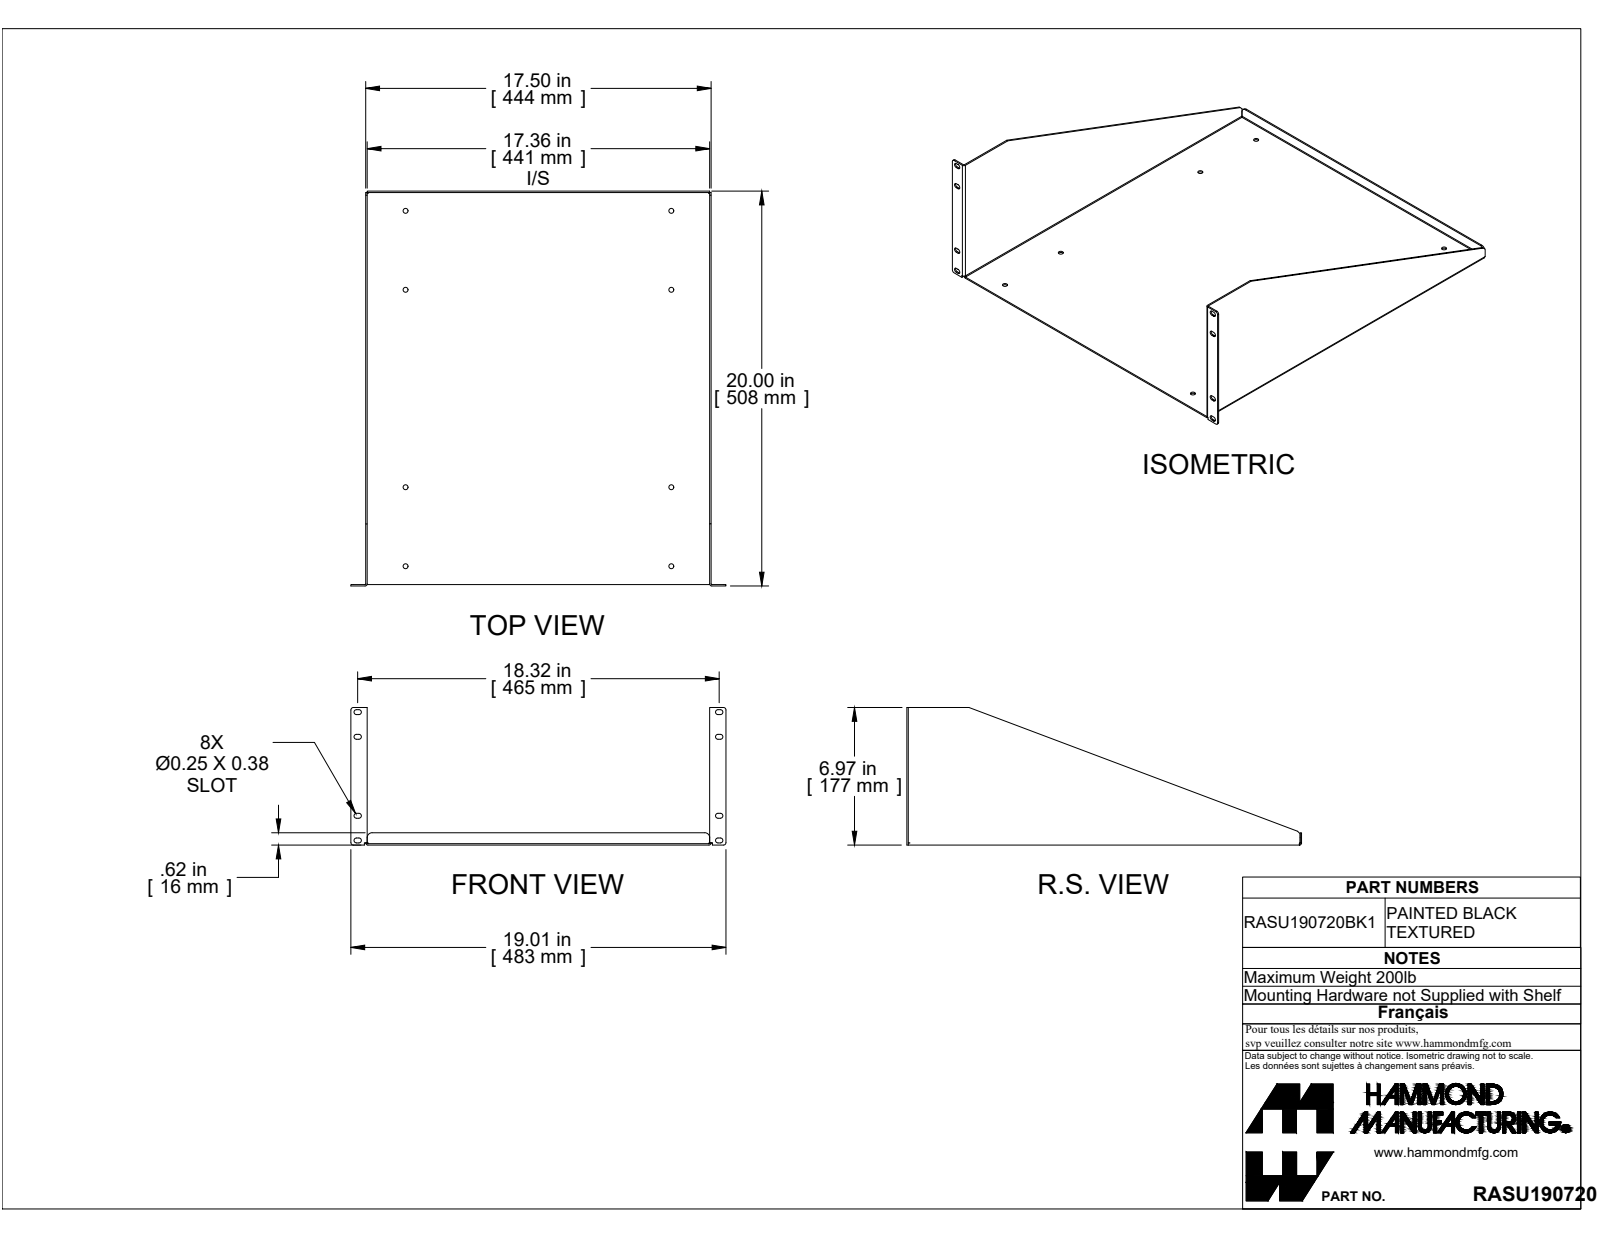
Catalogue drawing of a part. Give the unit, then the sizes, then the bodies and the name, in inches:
Units: inches
Overall size (bounding box): 20 × 19.006 × 6.968
Round holes (diameter × count): ⌀0.25 ×8
Partial cylindrical surfaces — rounded edges, fillets, slot ends (radius × count): R0.125 ×20, R0.036 ×5, R0.108 ×5, R0.055 ×3, R0.25 ×2
Main face-to-face distances: 0.072, 17.428, 17.356, 17.5, 0.072, 19.928, 20, 19.856, 19.928, 0.625
Hole centre spacings: 4, 13.468, 14, 14.049, 19.426, 10, 16.774, 18
Volume: 38.47 in³ · Surface area: 1 077 in²
Bodies: 1 solid, 104 faces (56 planar, 44 cylindrical, 4 other)
Part name (STEP PRODUCT): RASU190720BK1
STEP written by: SolidWorks 2019 (CONFIG_CONTROL_DESIGN)
